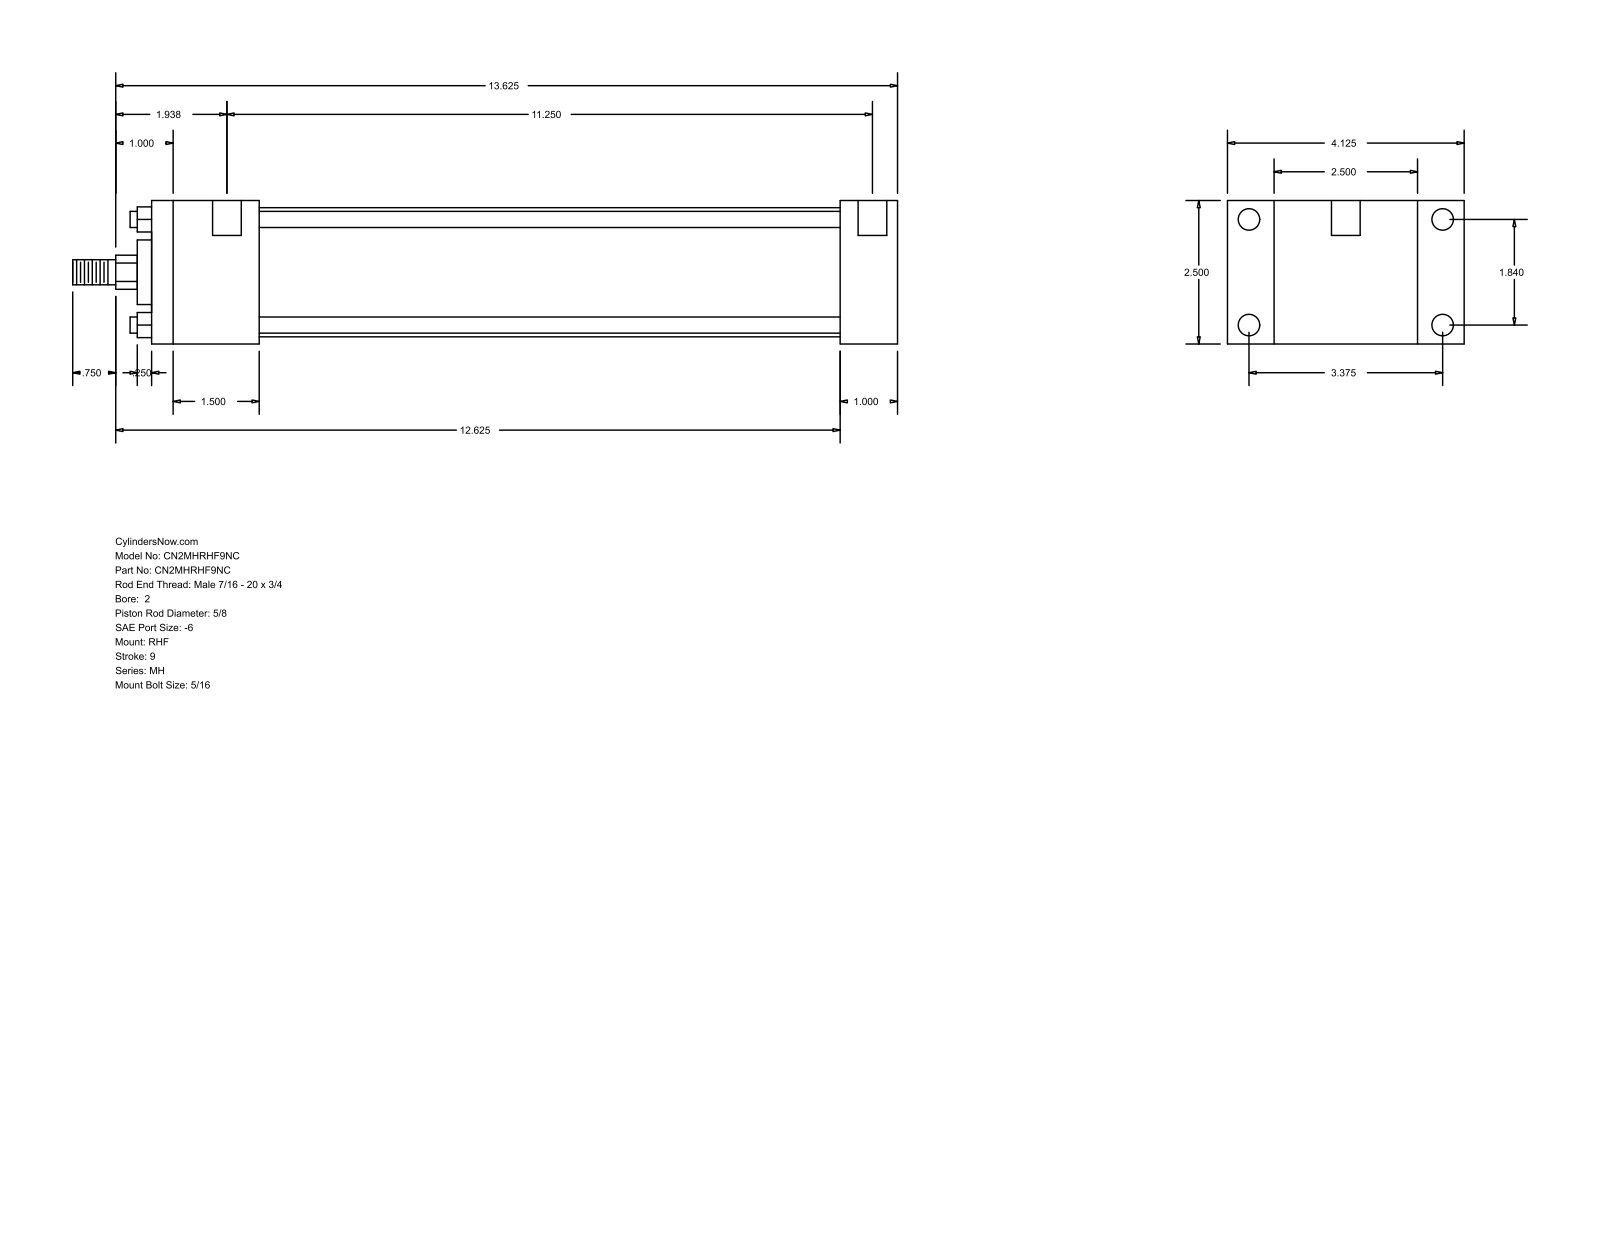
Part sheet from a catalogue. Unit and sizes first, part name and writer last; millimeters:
Units: millimetres
Overall size (bounding box): 365.12 × 104.78 × 63.5
Round holes (diameter × count): ⌀5.56 ×4, ⌀9.53 ×4, ⌀12.7 ×2
Round bosses / shafts (diameter × count): ⌀7.14 ×4, ⌀57.15 ×1, ⌀28.57 ×1, ⌀15.88 ×1, ⌀11.11 ×1
Partial cylindrical surfaces — rounded edges, fillets, slot ends (radius × count): R7.54 ×1
Main face-to-face distances: 63.5, 25.39, 20.64, 84.14, 304.8, 330.19, 104.78, 47.62, 257.18, 282.57
Hole centre spacings: 46.74, 85.72, 97.63, 293.69, 3.18, 4.76, 285.75, 288.93
Bodies: 0 solids, 88 faces (60 planar, 28 cylindrical, 0 other)
Part name (STEP PRODUCT): MH_RHF__0200_0.625
STEP written by: GSSL Pune (CONFIG_CONTROL_DESIGN)
